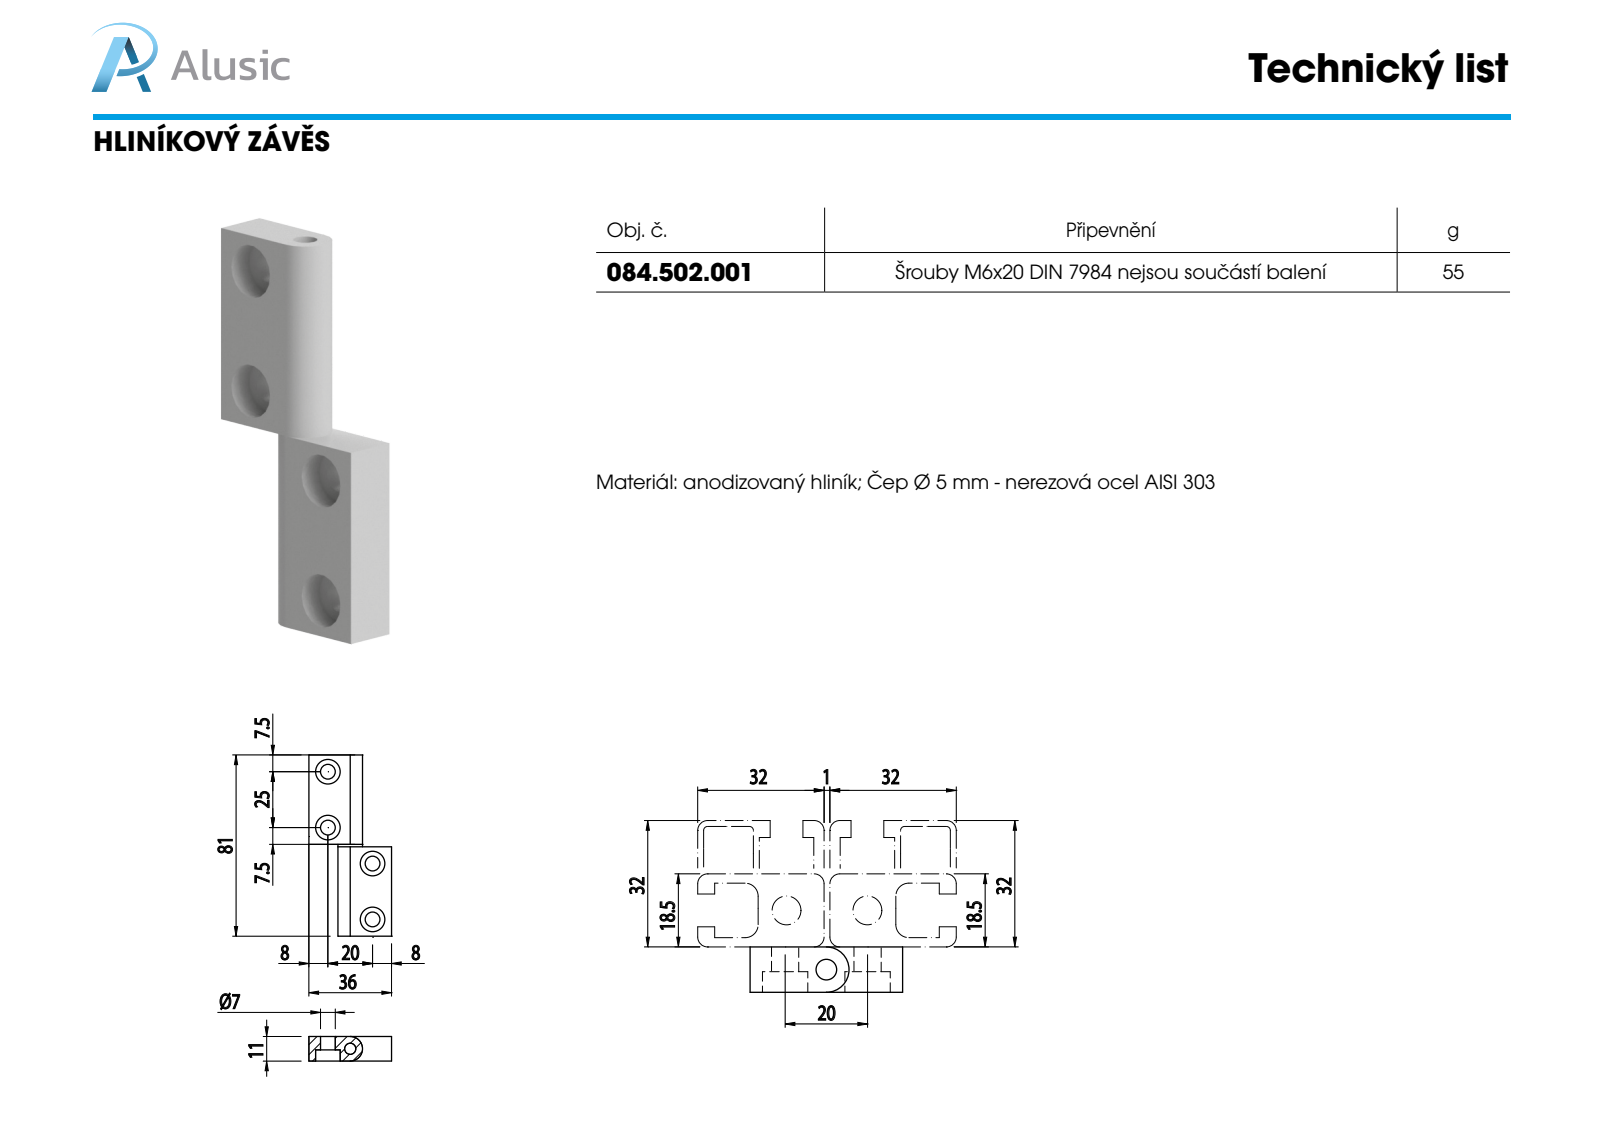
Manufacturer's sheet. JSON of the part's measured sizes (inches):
{"part_name": "084.502.000 ALETTE_ALETTA 1; 084.502.001", "step_written_by": "SolidWorks 2011 (CONFIG_CONTROL_DESIGN)", "units": "inches", "bodies": {"solids": 2, "faces": 36, "planar": 14, "cylindrical": 22, "other": 0}, "overall_size": [3.15, 1.457, 0.433], "volume_in3": 0.964, "surface_area_in2": 12.9, "round_holes": [[0.26, 4], [0.433, 4], [0.197, 1]], "round_bosses_or_shafts": [[0.433, 1]], "face_to_face_distances": [0.433, 1.575, 1.457, 0.236, 0.197, 3.15], "hole_center_spacings": [0.984, 1.761, 2.678]}
